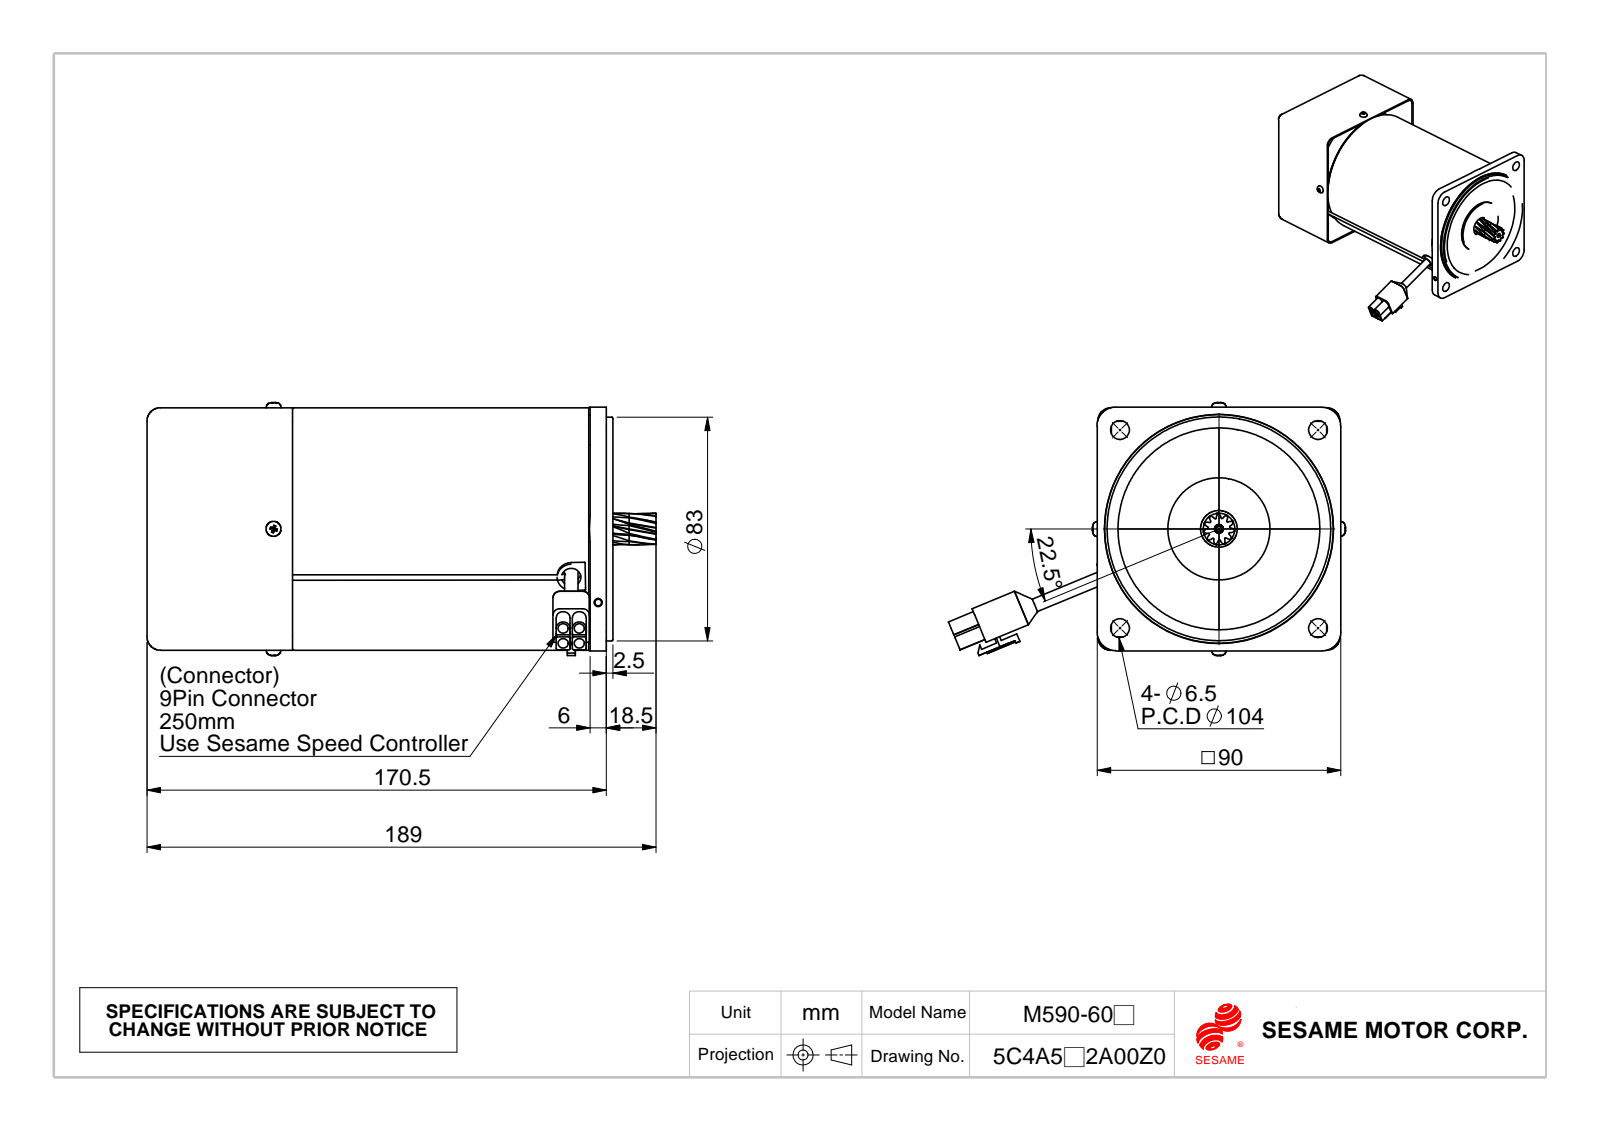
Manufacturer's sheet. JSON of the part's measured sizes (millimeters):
{"part_name": "M590-R-F; 90GX_1成品; 線扣; 獨立風扇220V 3K22200000 (+1 more)", "step_written_by": "SolidWorks 2010 (CONFIG_CONTROL_DESIGN)", "units": "millimeters", "bodies": {"solids": 14, "faces": 742, "planar": 273, "cylindrical": 269, "other": 200}, "overall_size": [189, 147.42, 93.92], "volume_mm3": 1074000, "surface_area_mm2": 148537, "round_holes": [[2.5, 5], [3.8, 4], [5.5, 4], [7, 4], [2, 2], [3, 2], [3.1, 2], [7.2, 1], [9.5, 1], [13.7, 1], [16, 1], [26, 1]], "round_bosses_or_shafts": [[5.5, 4], [11, 3], [3, 2], [2, 2], [90, 1], [87, 1], [86, 1], [84.15, 1]], "partial_cylinders_radius": [[0.3, 24], [0.5, 14], [0.25, 8], [4, 8], [5, 8], [2.5, 7], [1, 6], [2, 4]], "face_to_face_distances": [1, 89, 4, 5, 84, 85, 90, 88, 29, 12], "hole_center_spacings": [6, 3.6, 4.24, 5.01, 38.18, 52, 73.18, 73.54]}
